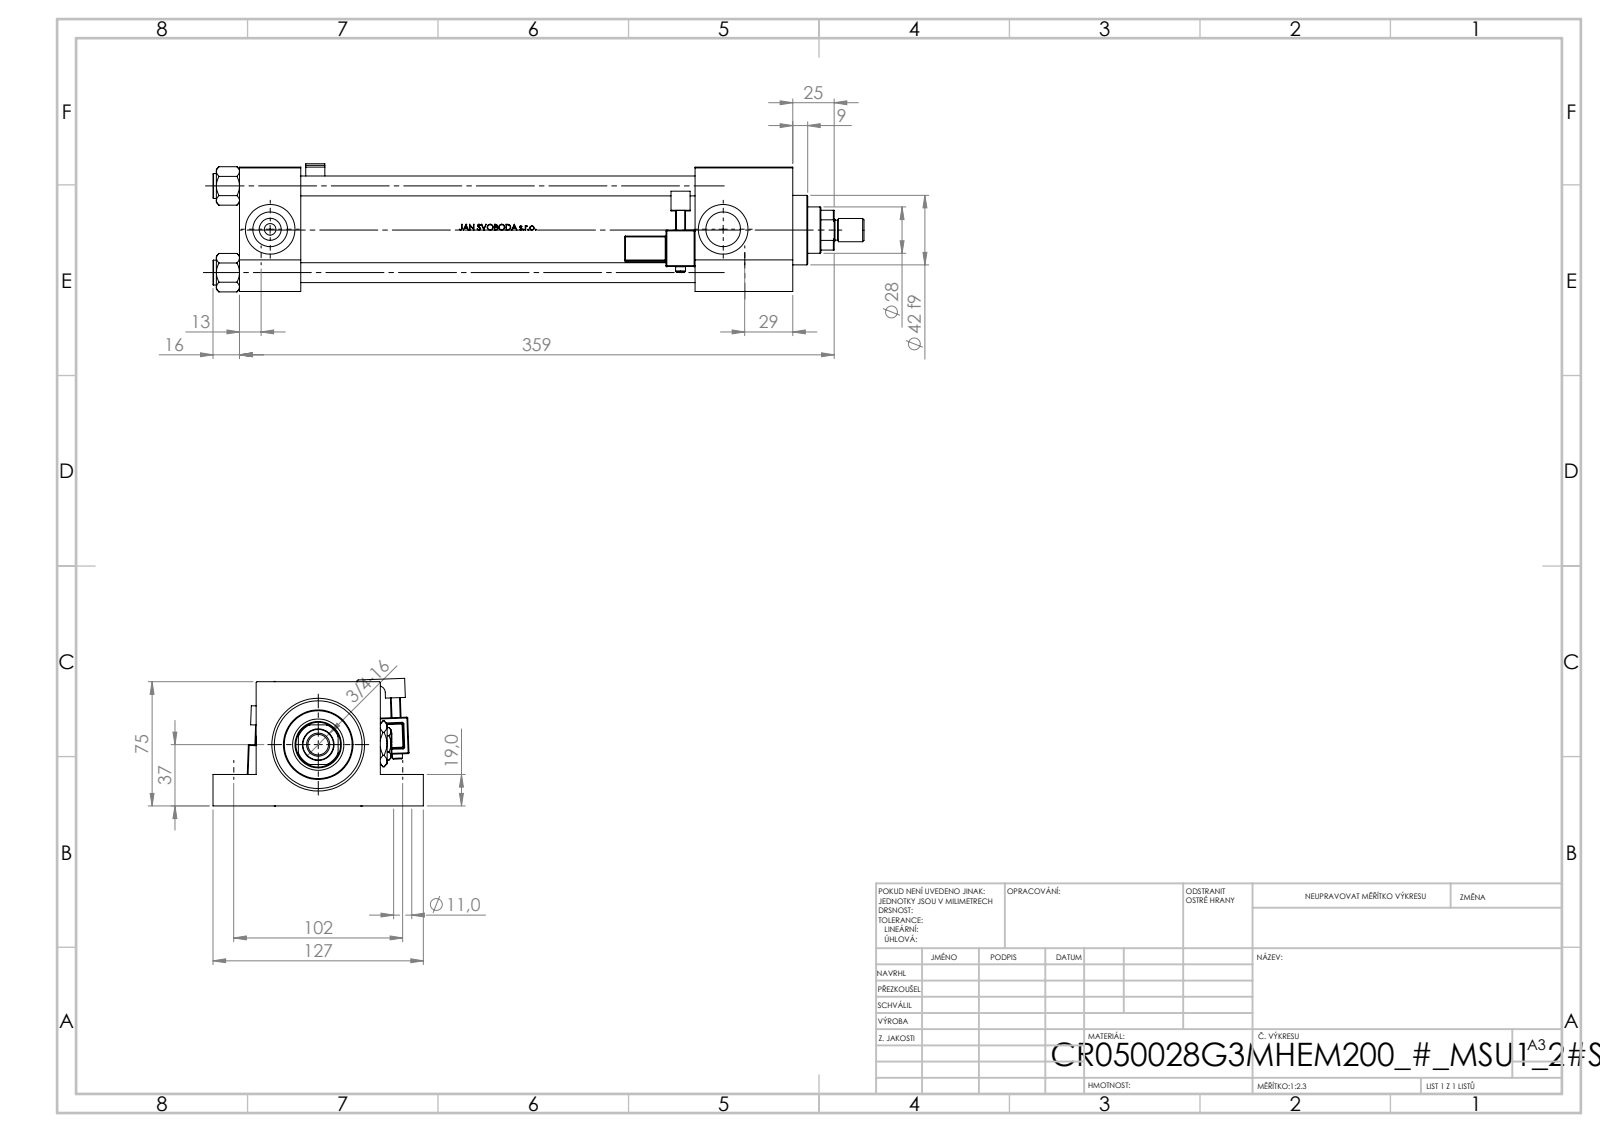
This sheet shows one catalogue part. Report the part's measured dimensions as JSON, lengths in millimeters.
{"part_name": "ROD_END_E; V215_VC_A; Zatka_pro_OIL_PORT; V215CR_MSU (+4 more)", "step_written_by": "SolidWorks 2019 (CONFIG_CONTROL_DESIGN)", "units": "millimeters", "bodies": {"solids": 16, "faces": 1351, "planar": 539, "cylindrical": 196, "other": 616}, "overall_size": [393, 127, 77.3], "volume_mm3": 1088000, "surface_area_mm2": 283876, "round_holes": [[11, 4], [12, 4], [7, 2], [20.96, 2], [30, 2], [18.5, 1], [28, 1], [31, 1], [41, 1], [50, 1], [53, 1]], "round_bosses_or_shafts": [[15, 4], [6, 2], [56, 1], [42, 1], [14, 1], [12, 1]], "partial_cylinders_radius": [[0.5, 48], [1, 2], [2.5, 2], [4, 2], [6, 1], [13.5, 1]], "face_to_face_distances": [75, 37, 334, 297, 56, 19, 275, 238, 59, 26], "hole_center_spacings": [52.3, 36.63, 37.34, 73.96, 102, 292, 309.3, 273.5]}
